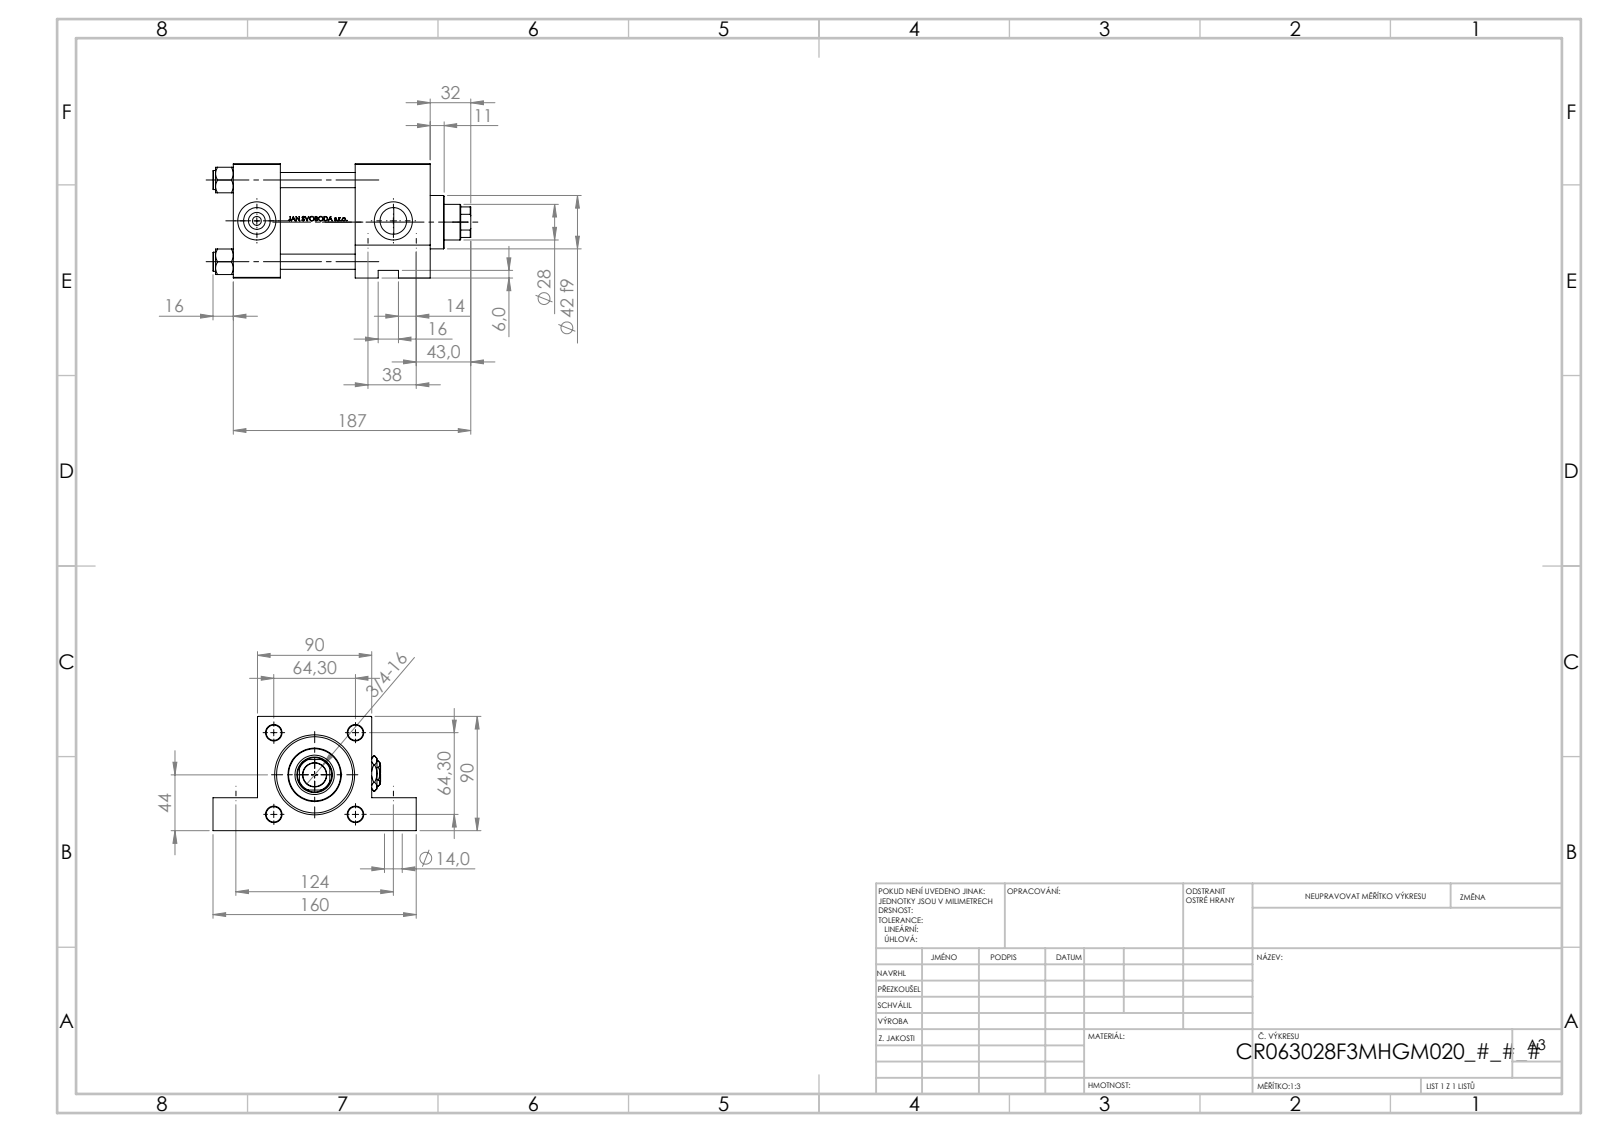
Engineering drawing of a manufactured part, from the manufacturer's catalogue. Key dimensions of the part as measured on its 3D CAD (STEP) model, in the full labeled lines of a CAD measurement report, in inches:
Part name (STEP PRODUCT): V215CR_F_TYCINKA; Zatka_pro_OIL_PORT; V215_VC_A; V215CR_F_Body (+2 more)
STEP written by: SolidWorks 2019 (CONFIG_CONTROL_DESIGN)
Units: inches
Bodies: 13 solids, 1200 faces (484 planar, 134 cylindrical, 582 other)
Overall size (bounding box): 7.992 × 6.299 × 3.543
Volume: 62.43 in³ · Surface area: 307.9 in²
Round holes (diameter × count): ⌀0.472 ×4, ⌀0.825 ×3, ⌀1.181 ×3, ⌀0.276 ×2, ⌀0.551 ×2, ⌀0.551 ×2, ⌀0.728 ×1, ⌀0.787 ×1, ⌀1.102 ×1, ⌀1.22 ×1, ⌀1.969 ×1, ⌀2.362 ×1
Round bosses / shafts (diameter × count): ⌀0.591 ×4, ⌀2.717 ×1, ⌀1.654 ×1
Partial cylindrical surfaces — rounded edges, fillets, slot ends (radius × count): R0.531 ×1
Main face-to-face distances: 3.543, 2.323, 1.457, 4.646, 6.102, 3.78, 0.787, 1.024, 2.52, 4.921
Hole centre spacings: 2.531, 1.496, 1.763, 1.818, 3.58, 4.882, 5.106, 0.394
